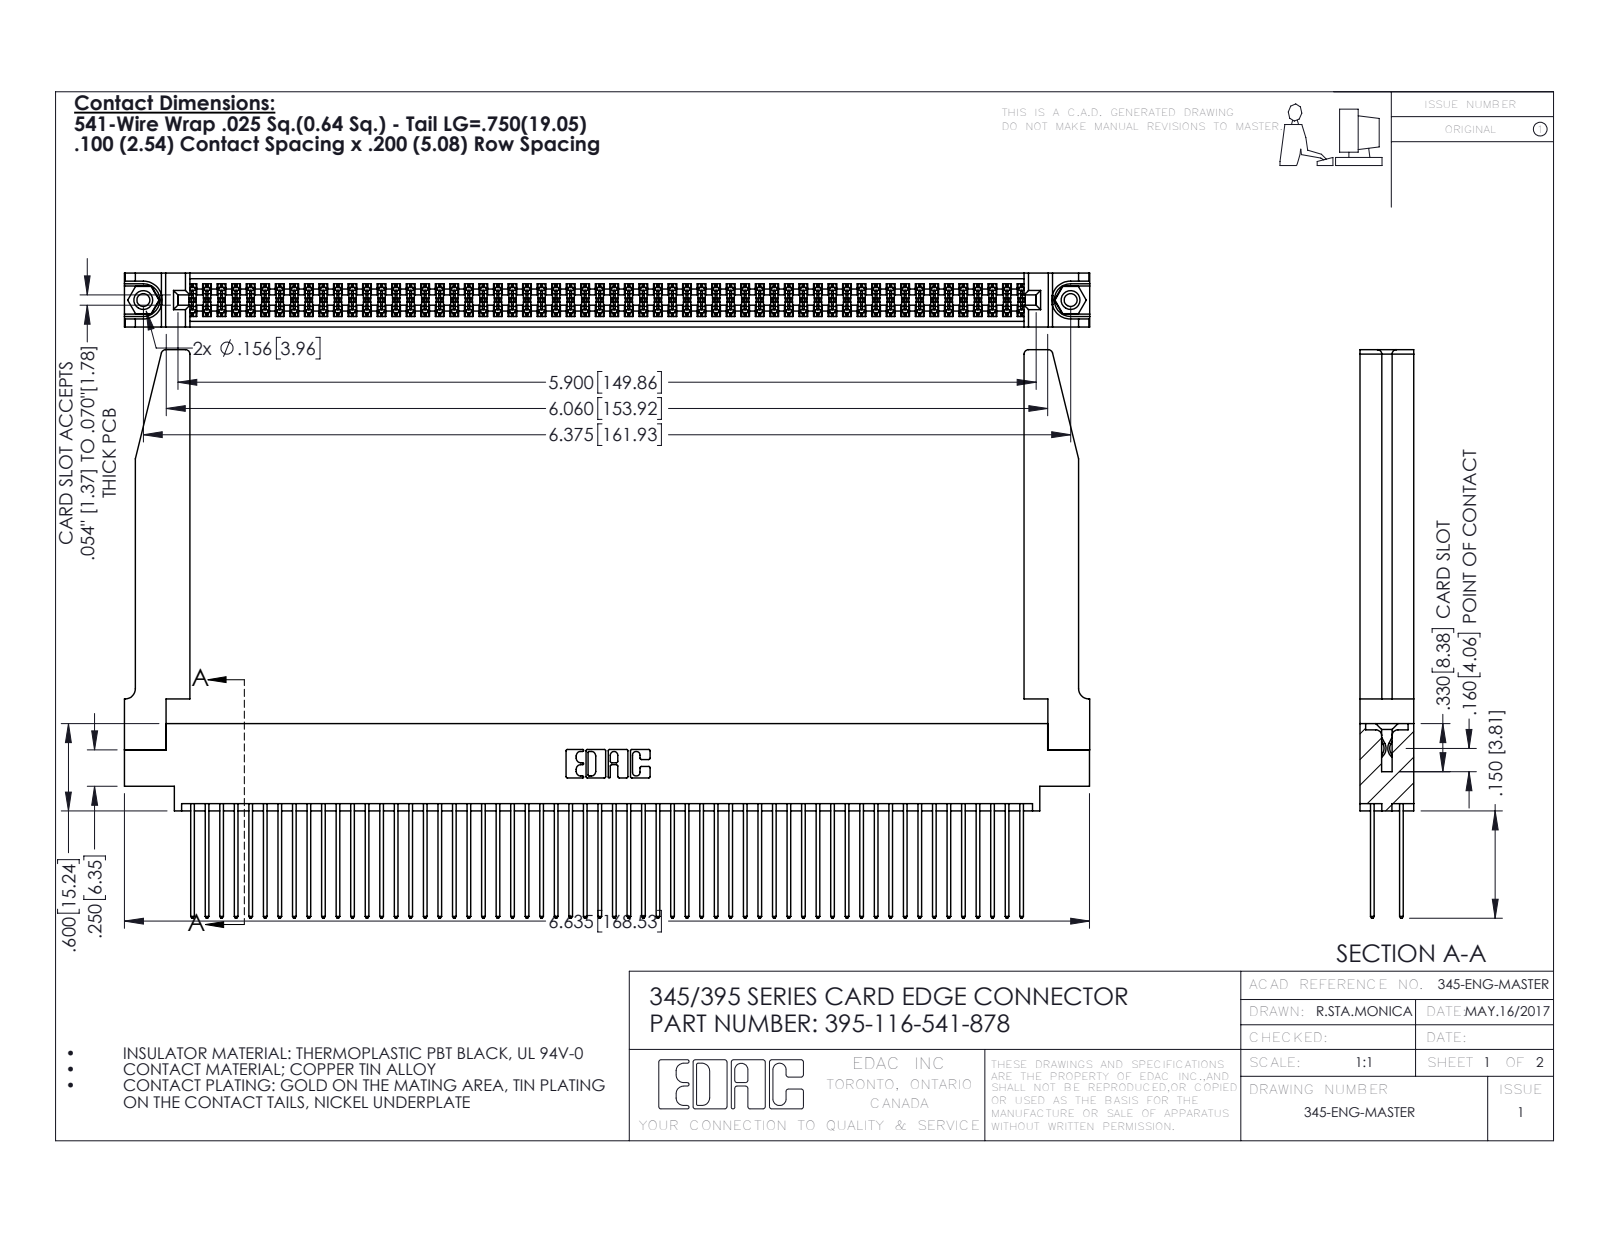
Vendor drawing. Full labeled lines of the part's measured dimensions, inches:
Part name (STEP PRODUCT): 345 Part_0.170 Offset - 0.156 Dia-TH; 345-250-001_345-250-001-102; 345-220-078_345-220-078; 345-292-001_345-293-141 (+1 more)
STEP written by: SolidWorks 2016 (CONFIG_CONTROL_DESIGN)
Units: inches
Bodies: 121 solids, 6164 faces (4054 planar, 2058 cylindrical, 52 other)
Overall size (bounding box): 6.636 × 3.907 × 0.37
Volume: 1.516 in³ · Surface area: 55.27 in²
Round holes (diameter × count): ⌀0.089 ×2, ⌀0.125 ×2, ⌀0.156 ×2, ⌀0.064 ×1
Round bosses / shafts (diameter × count): ⌀0.155 ×2
Partial cylindrical surfaces — rounded edges, fillets, slot ends (radius × count): R0.006 ×174, R0.01 ×116, R0.01 ×22, R0.03 ×8, R0.007 ×6, R0.031 ×6, R0.026 ×3, R0.014 ×2
Main face-to-face distances: 0.072, 0.298, 0.37, 0.098, 0.272, 0.025, 0.2, 0.225, 0.175, 0.15
Hole centre spacings: 0.27, 6.139, 6.375
